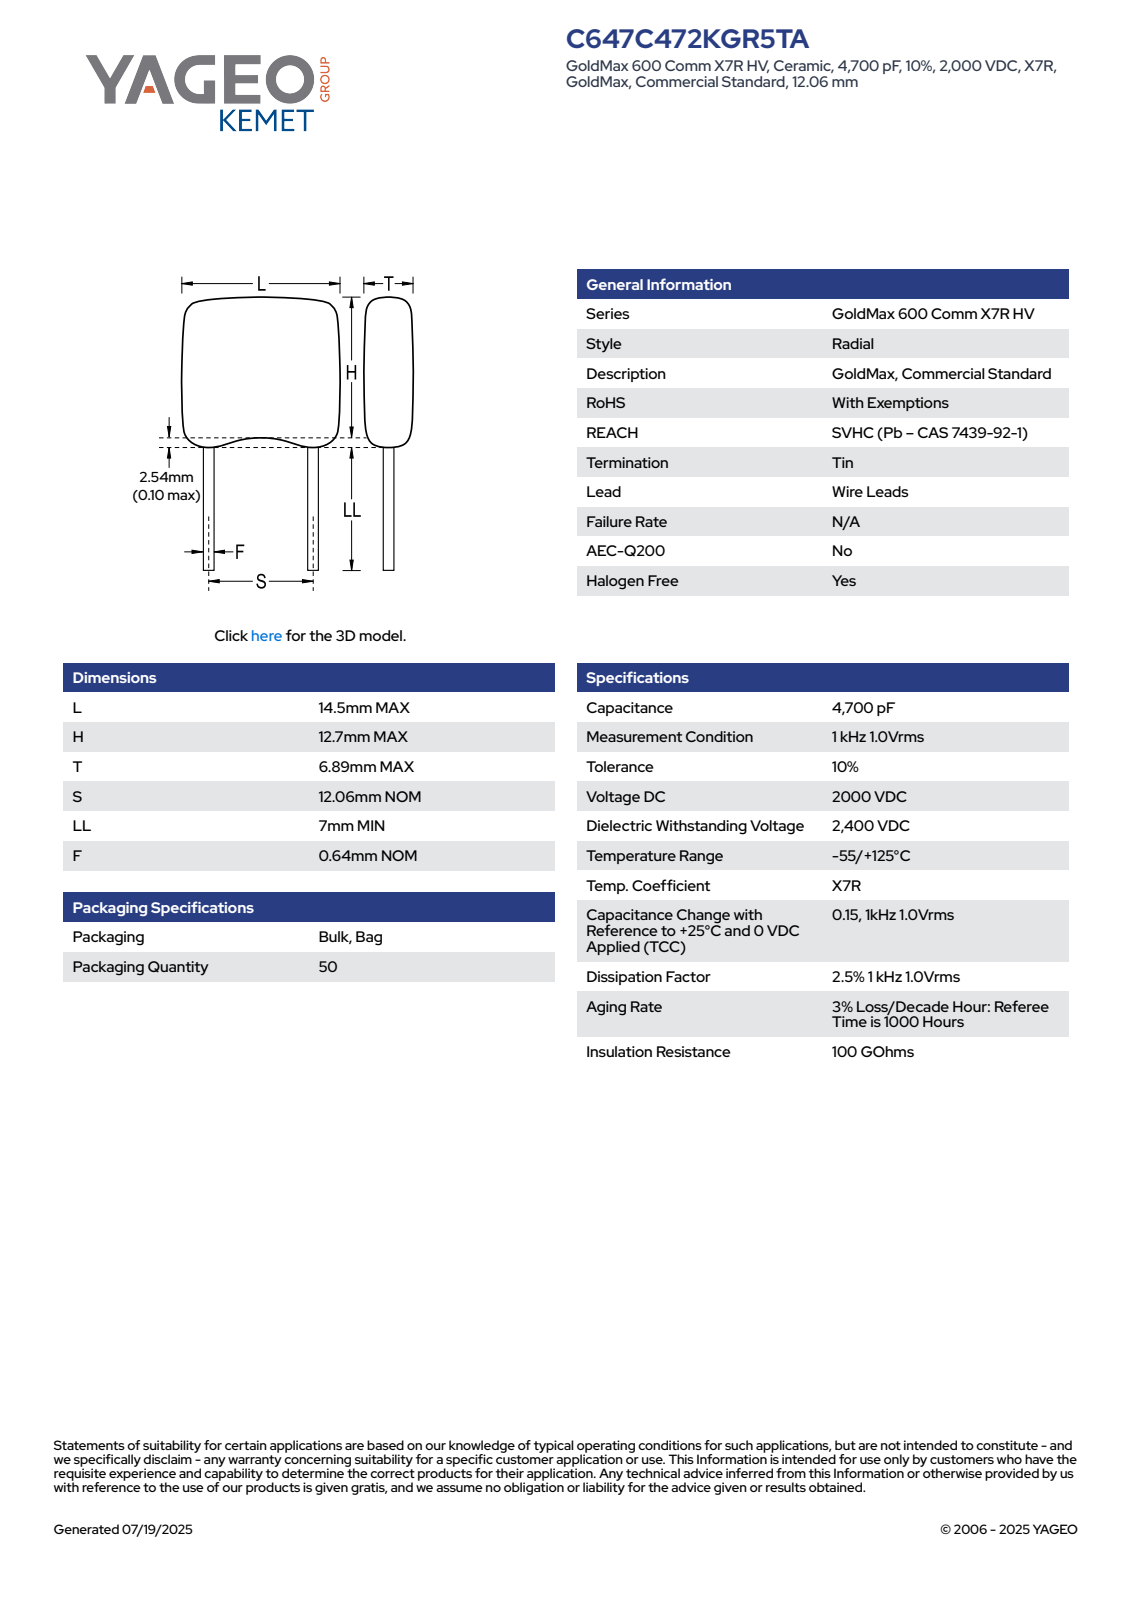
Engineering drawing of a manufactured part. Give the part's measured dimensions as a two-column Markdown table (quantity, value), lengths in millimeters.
| quantity | value |
| --- | --- |
| part name | CCR_KRCST_C647_L14.5H12.7T6.89S12.06LL7F0.64 |
| STEP written by | SolidWorks 2014 (AUTOMOTIVE_DESIGN) |
| units | millimeters |
| bodies | 4 solids, 83 faces (65 planar, 14 cylindrical, 4 other) |
| overall size | 21.22 × 14.5 × 6.89 |
| volume | 1 410 mm³ |
| surface area | 809 mm² |
| round bosses / shafts (diameter × count) | 0.64 × 2 |
| partial cylindrical surfaces (radius × count) | 0.75 × 10 |
| main face-to-face distances | 6.89, 14.5, 14.22, 7, 21.22, 15.2, 8.2, 6.02, 13.65, 6.65 |
